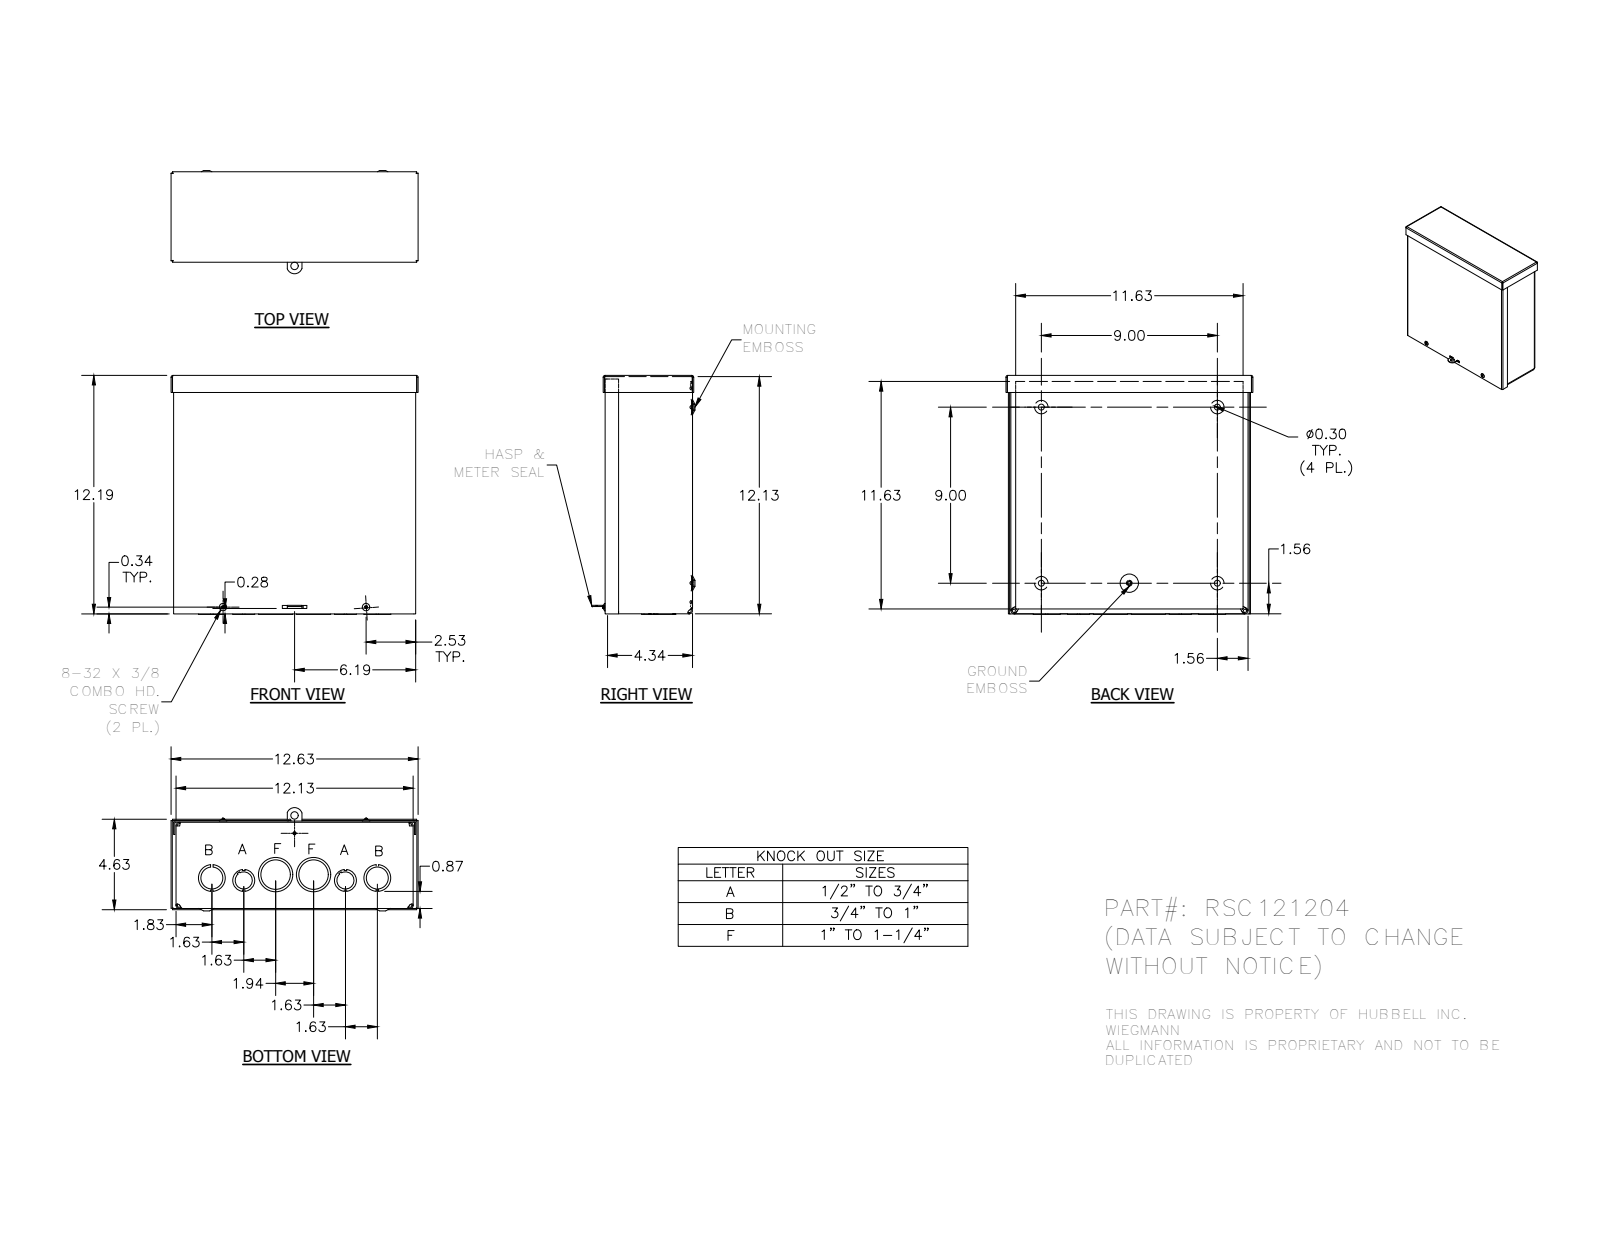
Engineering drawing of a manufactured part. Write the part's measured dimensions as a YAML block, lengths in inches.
part_name: "RSC121204; RSC121204_WRAP; RSC1212_LID; RSC1204_CAP (+4 more)"
step_written_by: "Autodesk Inventor 2012 (AUTOMOTIVE_DESIGN)"
units: inches
bodies: {solids: 7, faces: 551, planar: 264, cylindrical: 143, other: 144}
overall_size: [12.625, 12.281, 5.125]
volume: 40.55
surface_area: 1327
round_holes:
  - {diameter: 0.3, count: 4}
  - {diameter: 0.313, count: 4}
  - {diameter: 1.125, count: 4}
  - {diameter: 0.125, count: 2}
  - {diameter: 0.148, count: 2}
  - {diameter: 0.875, count: 2}
  - {diameter: 1.375, count: 2}
  - {diameter: 1.5, count: 2}
  - {diameter: 1.75, count: 2}
  - {diameter: 0.156, count: 1}
  - {diameter: 0.165, count: 1}
  - {diameter: 0.375, count: 1}
round_bosses_or_shafts:
  - {diameter: 0.384, count: 2}
  - {diameter: 0.164, count: 2}
  - {diameter: 0.229, count: 1}
partial_cylinders:
  - {radius: 0.01, count: 14}
  - {radius: 0.031, count: 8}
  - {radius: 0.093, count: 8}
  - {radius: 0.125, count: 8}
  - {radius: 0.187, count: 8}
  - {radius: 0.031, count: 6}
  - {radius: 0.025, count: 5}
  - {radius: 0.055, count: 4}
face_to_face_distances: [0.062, 12.126, 4.249, 4.187, 0.062, 0.063, 4.312, 4.25, 12.188, 0.124]
hole_center_spacings: [9, 1.356, 1.635, 1.656, 3.031, 3.264, 3.582, 4.5]
